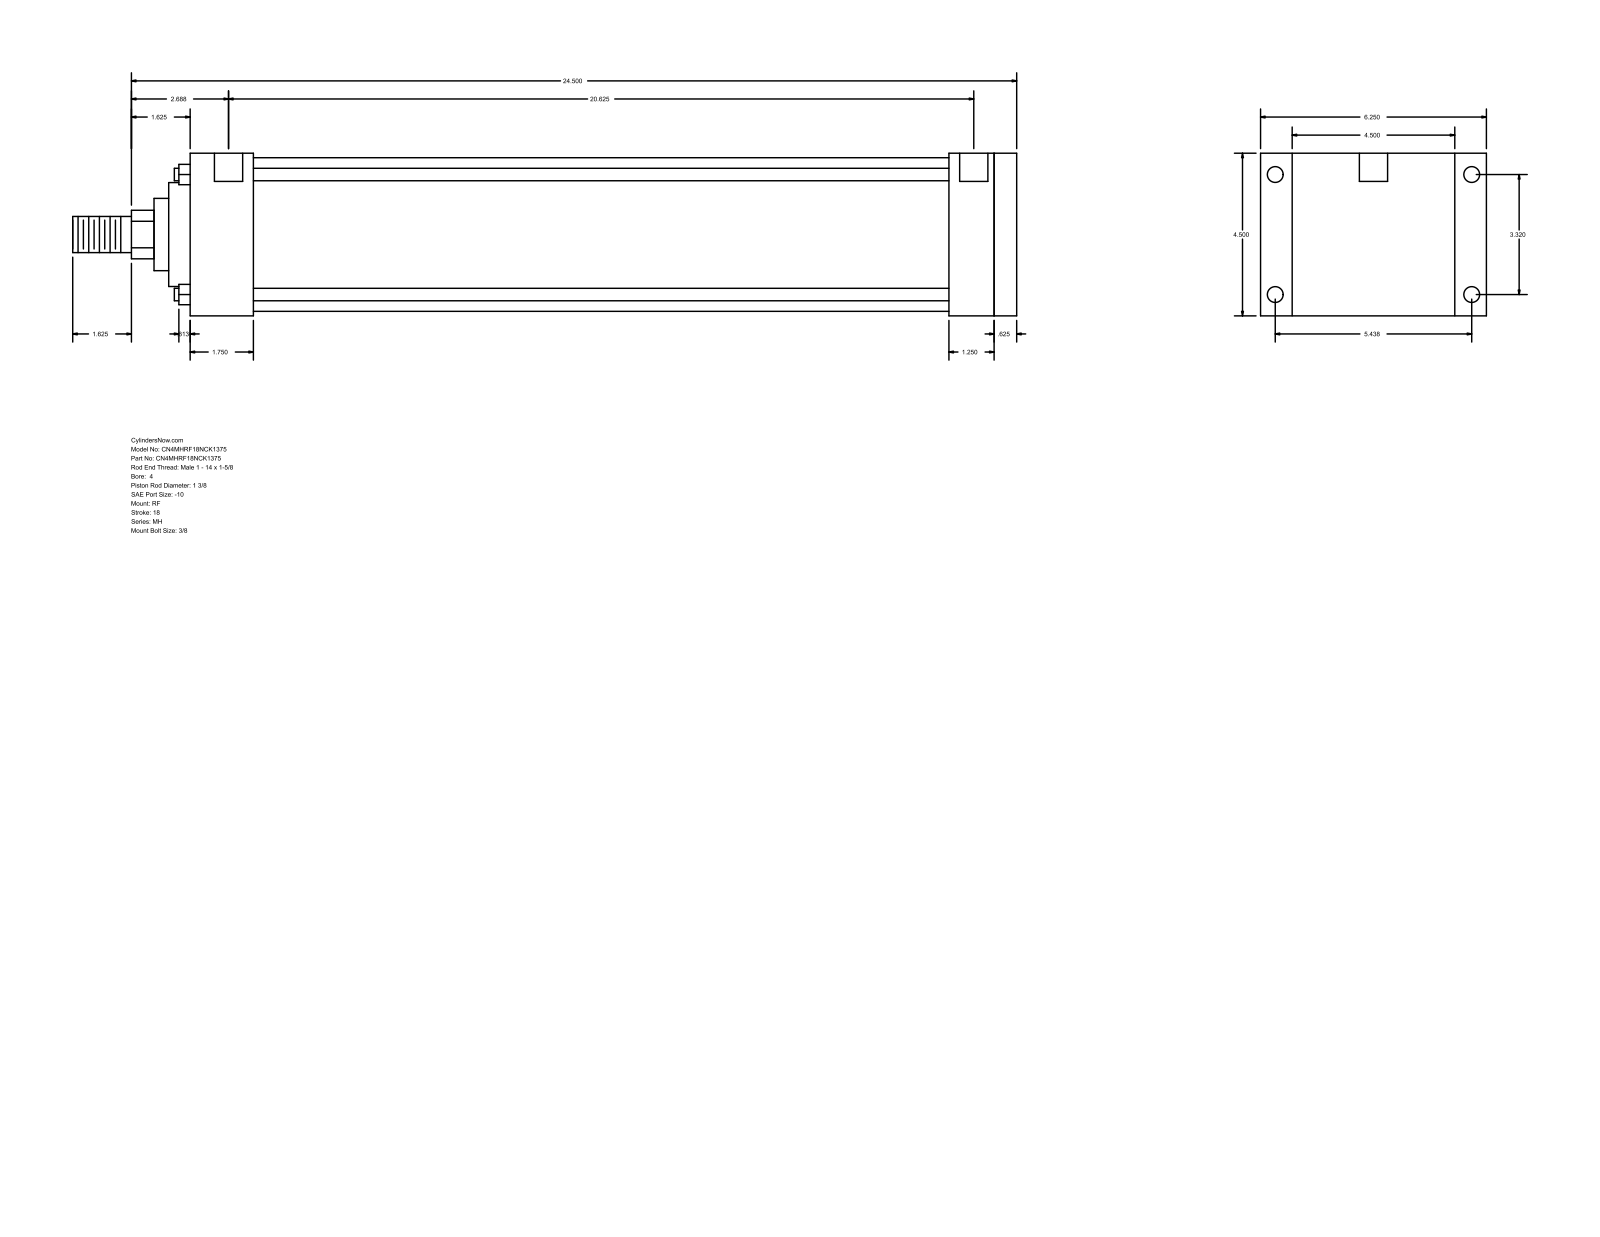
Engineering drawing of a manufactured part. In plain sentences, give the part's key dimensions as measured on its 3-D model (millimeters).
The part is named "MH_RF__0400_1.375". Its 3-D file was written by "GSSL Pune (CONFIG_CONTROL_DESIGN)". It is 0 solids with 94 faces: 65 planar, 29 cylindrical and 0 other. Overall it measures 663.58 by 158.75 by 114.3 millimeters. Round holes: 4 of diameter 8.73, 4 of diameter 11.13, 2 of diameter 19.84. Round bosses or shafts: 4 of diameter 8.76, 1 of diameter 107.95, 1 of diameter 73.03, 1 of diameter 50.8, 1 of diameter 34.92, 1 of diameter 25.4. Partial cylindrical surfaces (rounded edges, fillets, slot ends): 1 of radius 17.06. The main face-to-face distances are 114.3, 581.03, 15.88, 565.15, 44.45, 520.7, 536.58, 533.4, 488.95, 31.75. The hole center spacings are 1.59, 84.32, 138.12, 161.82, 525.47, 527.06, 523.88.
